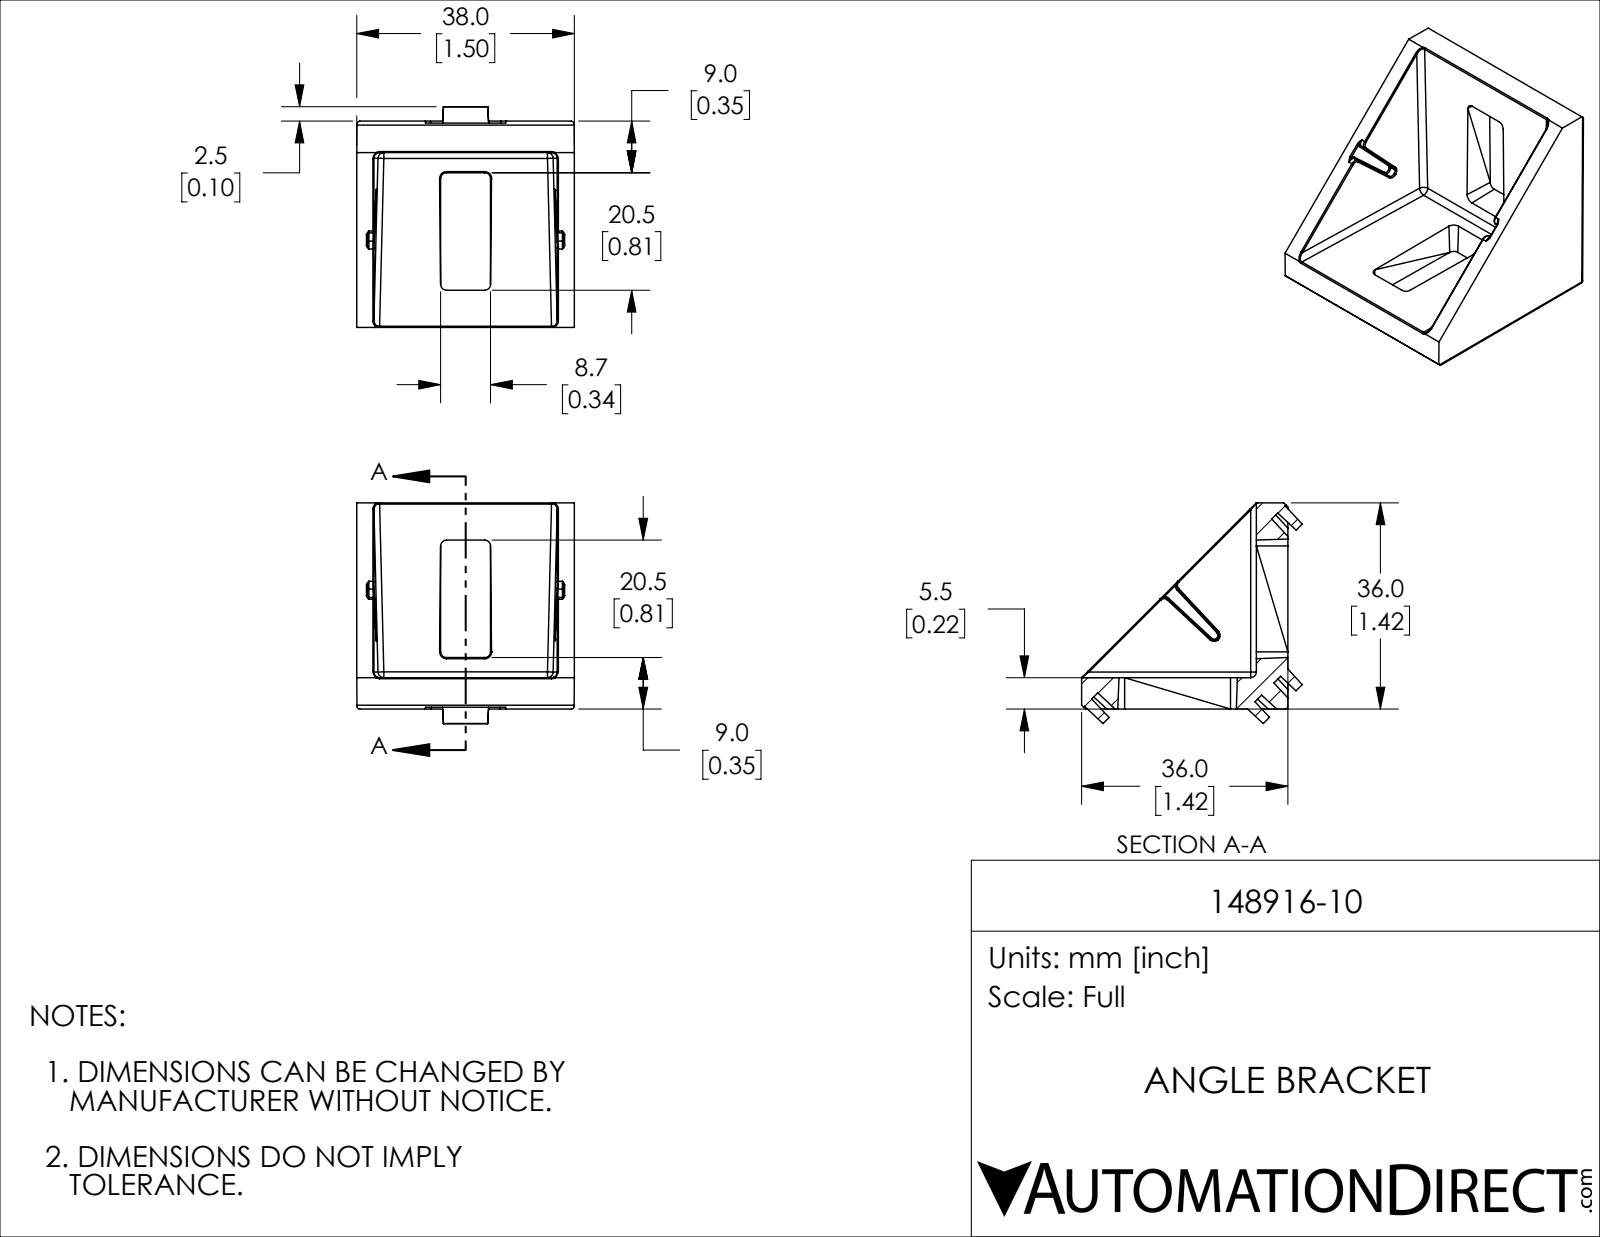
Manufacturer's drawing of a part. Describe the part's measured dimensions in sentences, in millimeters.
The part is named "148916-10". Its 3-D file was written by "SolidWorks 2024 (CONFIG_CONTROL_DESIGN)". It is 1 solid with 387 faces: 110 planar, 149 cylindrical and 128 other. Overall it measures 38.52 by 38.52 by 38 millimeters. Its volume is 12 878 cubic millimeters and its surface area 8 696 square millimeters. Partial cylindrical surfaces (rounded edges, fillets, slot ends): 66 of radius 0.3, 15 of radius 1, 14 of radius 0.2, 11 of radius 0.5, 1 of radius 0.86. The main face-to-face distances are 5.5, 30.5, 36, 33, 2.5, 3, 23.97, 8.7, 20.5, 19.22.
